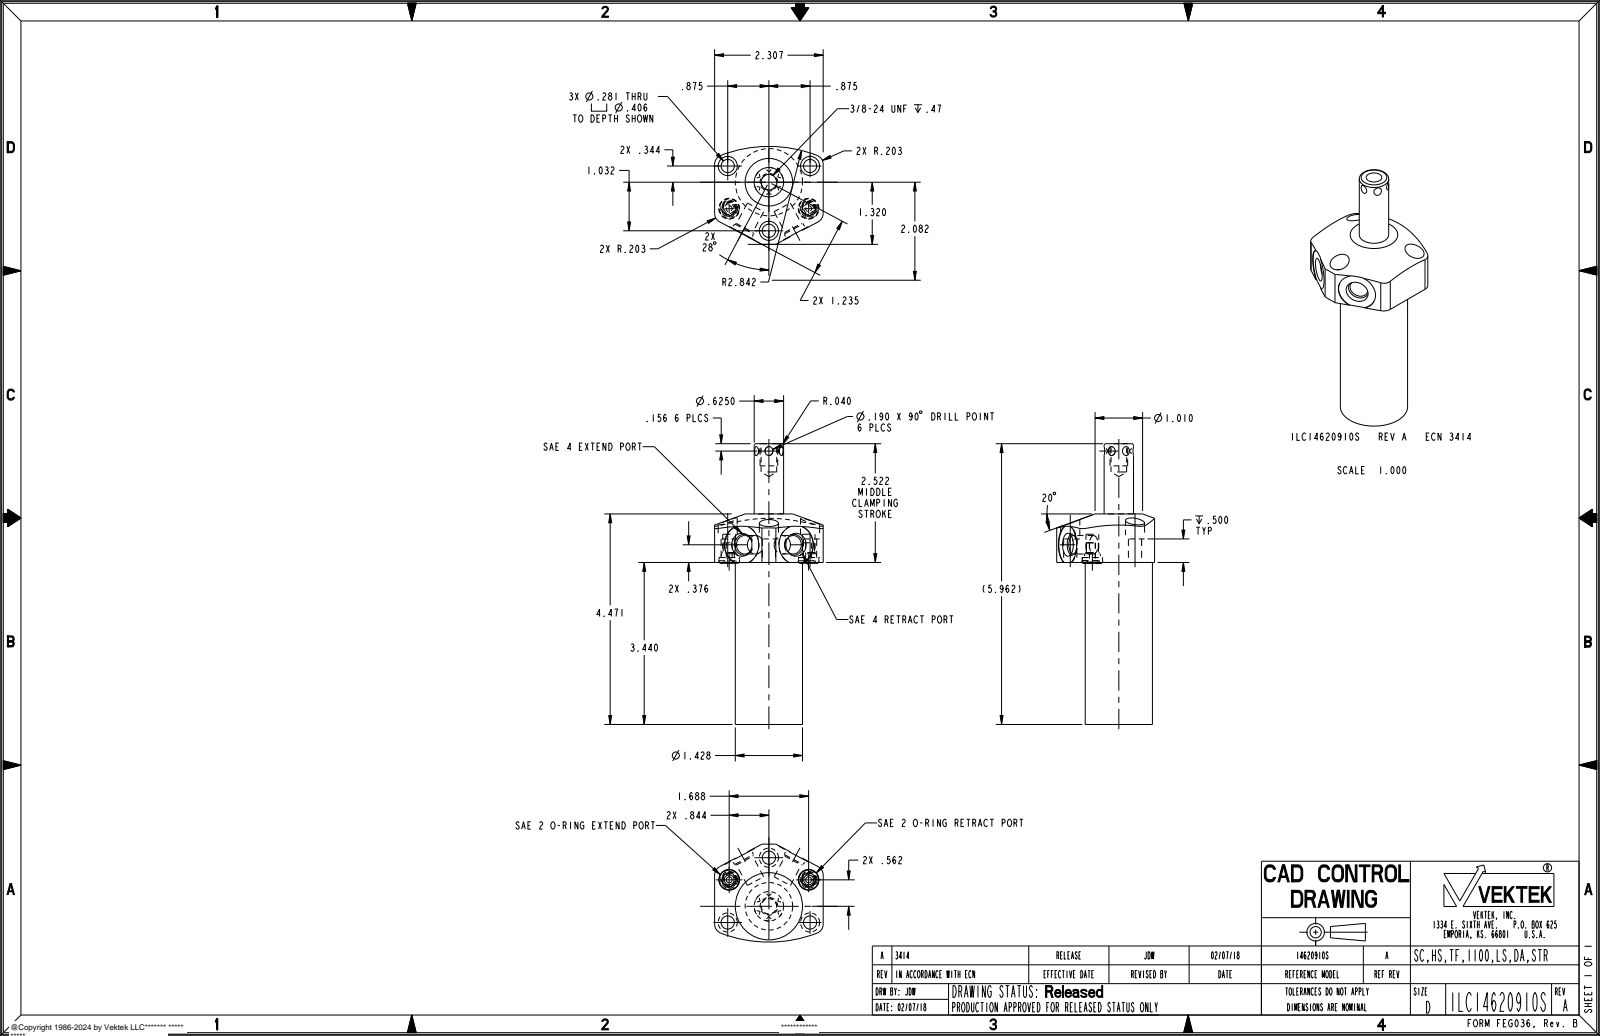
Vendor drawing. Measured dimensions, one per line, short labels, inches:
name: ILC14620910S
written by: PRO/ENGINEER BY PARAMETRIC TECHNOLOGY CORPORATION, 2013320 (AUTOMOTIVE_DESIGN)
unit: in
bodies: 1 solid, 132 faces (33 planar, 57 cylindrical, 42 other)
size: 5.962 × 2.307 × 2.08
volume: 9.184 in³; area: 40.39 in²
holes: 3× ⌀0.281, 3× ⌀0.406, 2× ⌀0.125, 2× ⌀0.272, 2× ⌀0.392, 2× ⌀0.438, 1× ⌀0.332
bosses: 2× ⌀0.43, 2× ⌀0.256, 2× ⌀0.21, 1× ⌀1.428, 1× ⌀0.625, 1× ⌀0.375
rounds: 4× R0.203, 2× R0.412, 1× R2.842
face distances: 3.44, 2.307, 4.471, 1.031, 0.62, 3.94, 0.5, 0.531, 0.1, 0.495
hole spacings: 0.906, 0.94, 0.966, 1.014, 1.631, 1.943, 1.032, 1.688
